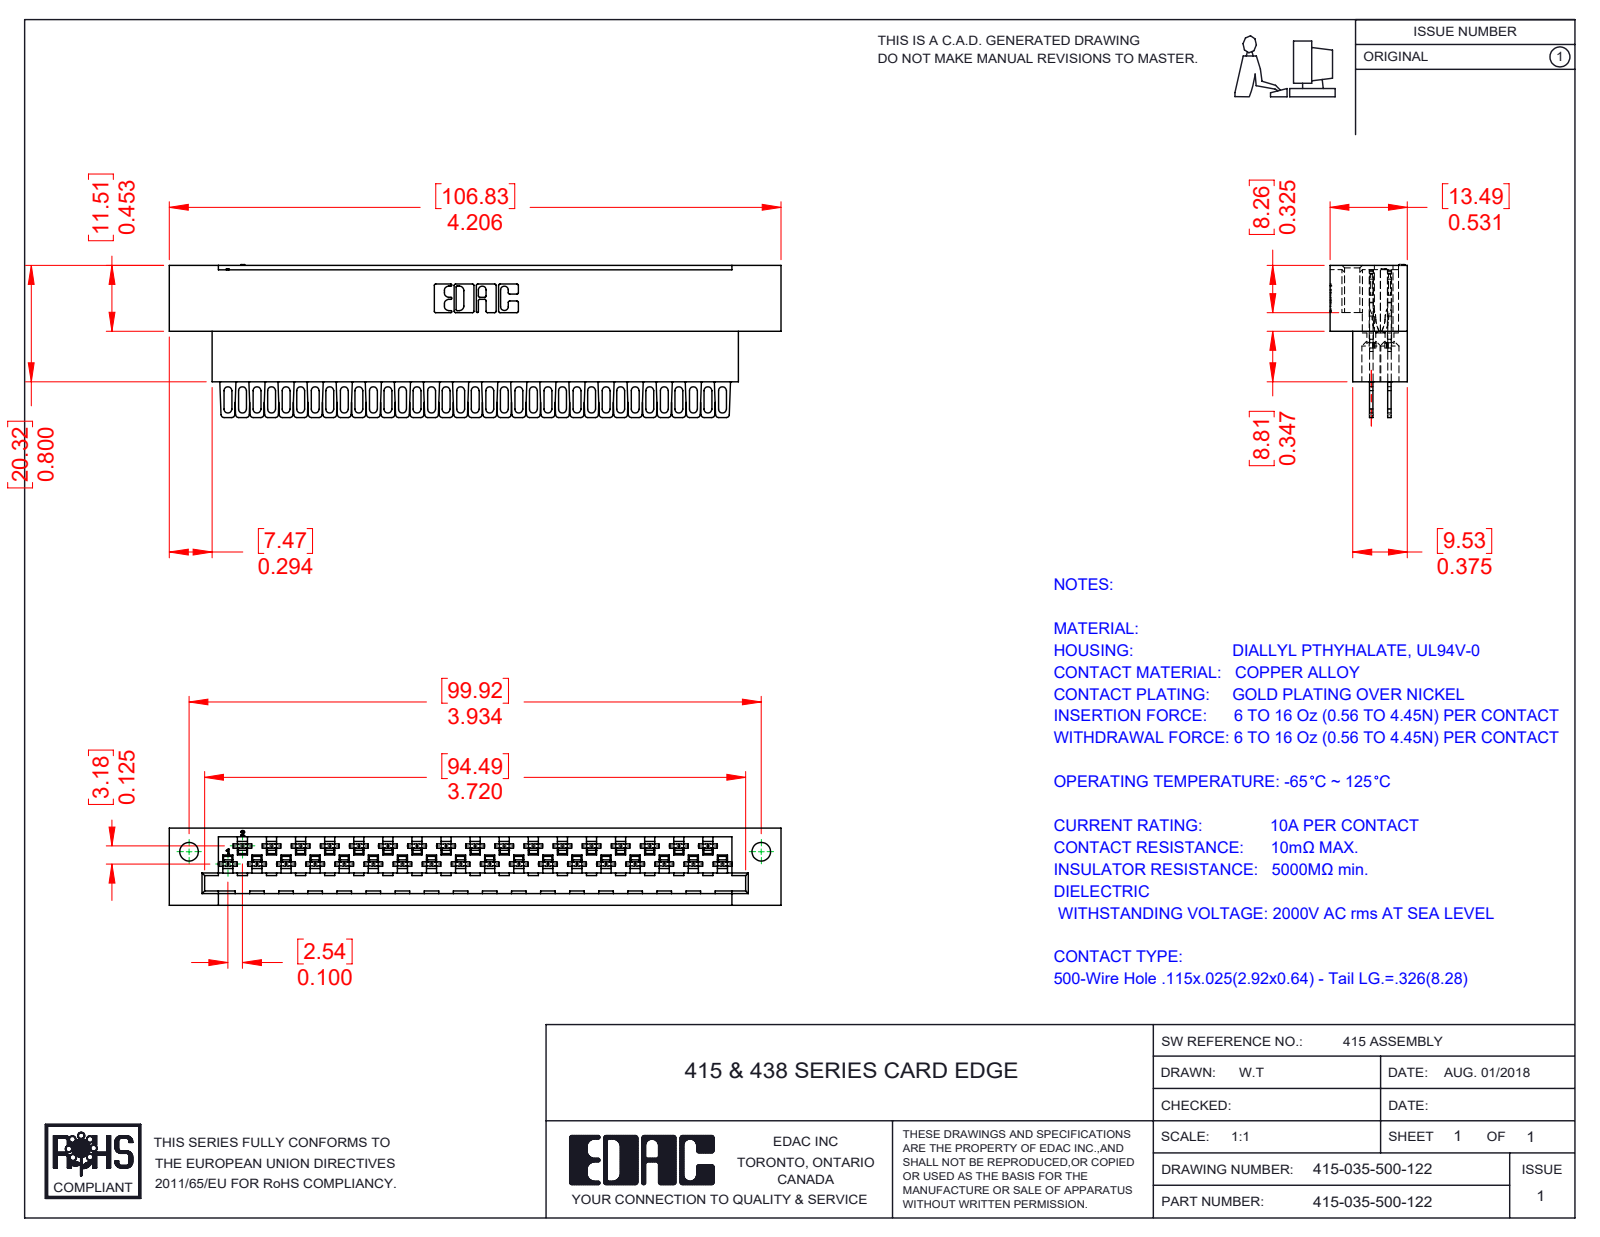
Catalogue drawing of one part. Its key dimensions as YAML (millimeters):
part_name: "415-035-500-122; 415-210-001_415-210-035-122; 516-290-001_500"
step_written_by: "SolidWorks 2016 (CONFIG_CONTROL_DESIGN)"
units: millimeters
bodies: {solids: 36, faces: 3714, planar: 2318, cylindrical: 1059, other: 337}
overall_size: [106.83, 26.68, 13.49]
volume: 17533
surface_area: 22806
round_holes:
  - {diameter: 1.27, count: 35}
  - {diameter: 3.3, count: 35}
  - {diameter: 3.25, count: 2}
partial_cylinders:
  - {radius: 0.3, count: 140}
  - {radius: 0.56, count: 140}
  - {radius: 0.18, count: 70}
  - {radius: 0.2, count: 70}
  - {radius: 0.41, count: 70}
  - {radius: 0.51, count: 70}
  - {radius: 0.69, count: 70}
  - {radius: 2.03, count: 70}
face_to_face_distances: [3.18, 0.61, 7.49, 1.27, 1.88, 13.49, 6.61, 6.88, 6, 2.82]
hole_center_spacings: [5.08, 10.16, 15.24, 20.32, 25.4, 30.48, 35.56, 2.54]
